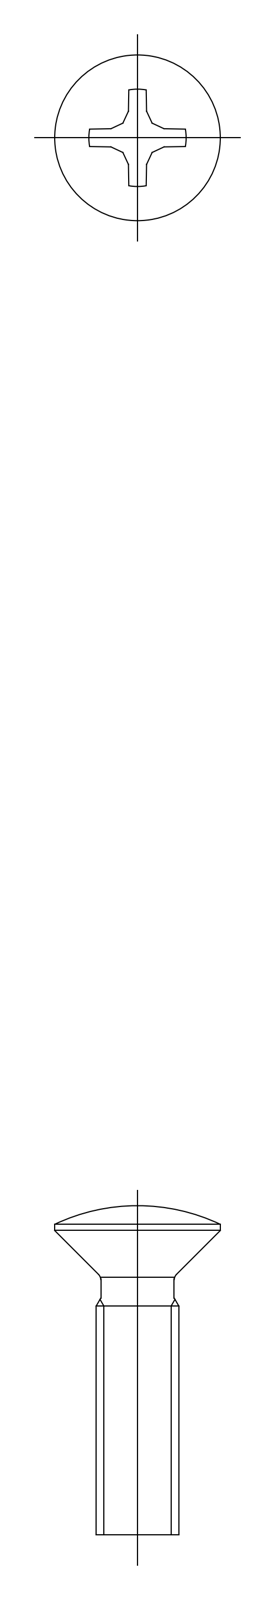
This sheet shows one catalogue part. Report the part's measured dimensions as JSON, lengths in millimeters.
{"part_name": "screw", "step_written_by": "CADfix (AUTOMOTIVE_DESIGN)", "units": "millimeters", "bodies": {"solids": 1, "faces": 27, "planar": 0, "cylindrical": 0, "other": 27}, "overall_size": [15.88, 8, 8], "volume_mm3": 247, "surface_area_mm2": 299}
